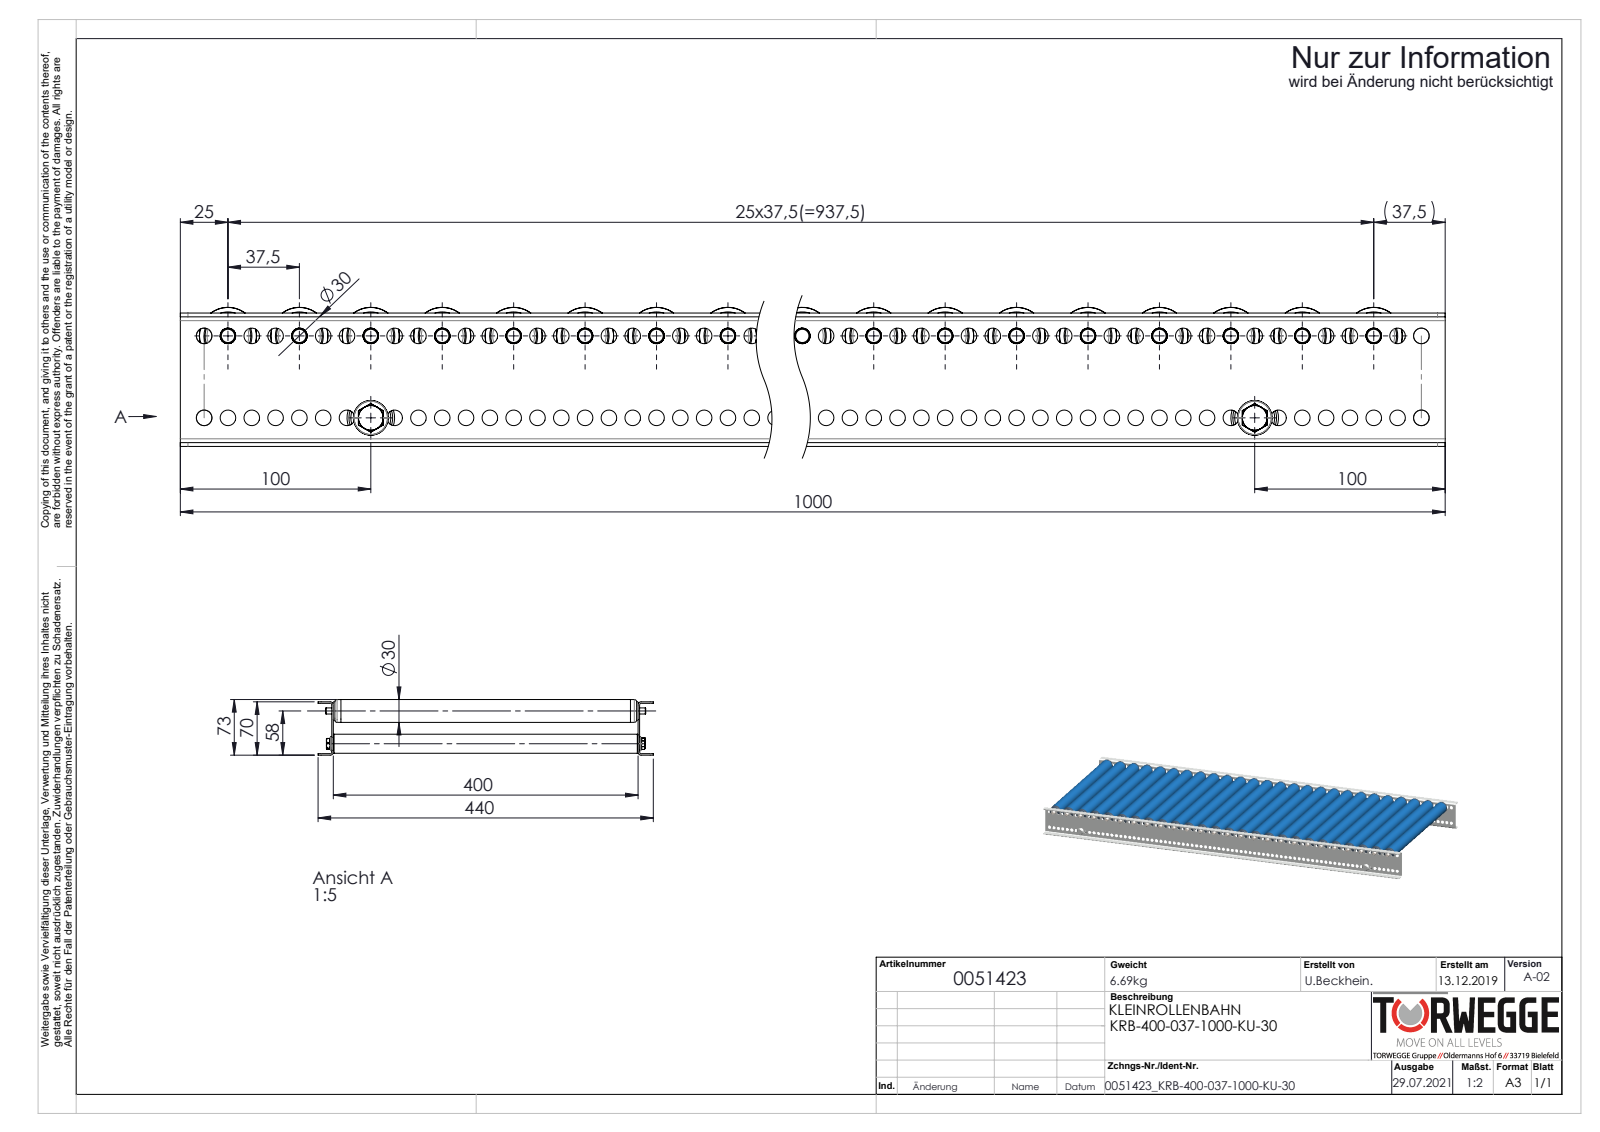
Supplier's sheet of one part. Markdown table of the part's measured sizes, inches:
| quantity | value |
| --- | --- |
| part name | S100995_TYP-KUT50-30x1,8-A8; 0039778-Achse-ST-Ø08-KFG_AL420-G-FA; Traversen_KFG_L400; 0017013_Tragrollenrohr-Ø30x1,8KU_KFG_L=380 (+4 more) |
| STEP written by | SolidWorks 2020 (AUTOMOTIVE_DESIGN) |
| units | inches |
| bodies | 64 solids, 6268 faces (1940 planar, 2352 cylindrical, 1976 other) |
| overall size | 39.37 × 17.323 × 2.874 |
| volume | 161.5 in³ |
| surface area | 4 452 in² |
| round holes (diameter × count) | 0.323 × 158, 0.319 × 26, 0.89 × 26, 0.992 × 26, 0.268 × 2, 0.827 × 2 |
| round bosses / shafts (diameter × count) | 0.315 × 28, 1.181 × 26, 1.177 × 26, 1.043 × 26, 1.039 × 26, 0.945 × 26, 0.984 × 2 |
| partial cylindrical surfaces (radius × count) | 0.199 × 26, 0.157 × 8, 0.079 × 4 |
| main face-to-face distances | 0.079, 15.827, 15.748, 2.677, 15.906, 2.598, 2.756, 0.394, 15.354, 0.472 |
| hole center spacings | 0.492, 0.984, 1.476, 1.969, 2.461, 2.953, 3.445, 3.937 |
